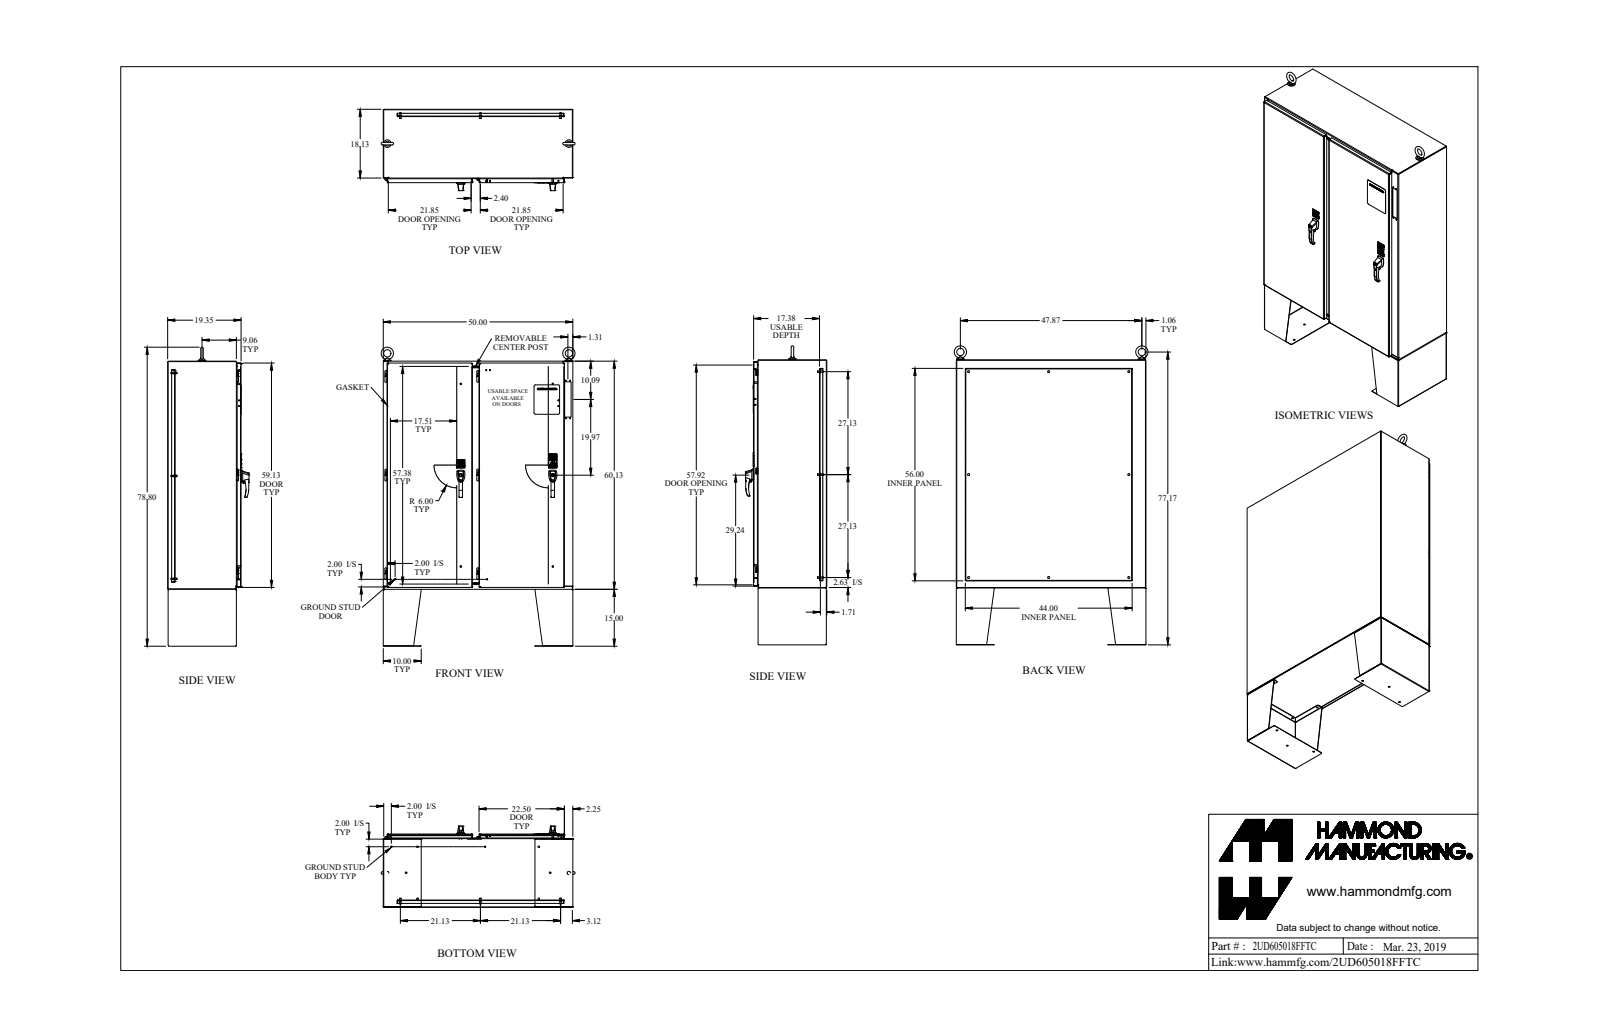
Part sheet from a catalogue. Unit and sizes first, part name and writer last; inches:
Units: inches
Overall size (bounding box): 78.799 × 51.122 × 21.466
Round holes (diameter × count): ⌀0.437 ×14, ⌀0.196 ×11, ⌀0.281 ×11, ⌀0.307 ×11, ⌀0.25 ×10, ⌀0.35 ×8, ⌀0.257 ×6, ⌀0.313 ×6, ⌀0.445 ×5, ⌀0.28 ×4, ⌀0.282 ×4, ⌀0.375 ×4
Round bosses / shafts (diameter × count): ⌀0.25 ×19, ⌀1 ×14, ⌀0.375 ×9, ⌀0.33 ×9, ⌀0.281 ×8, ⌀0.75 ×6, ⌀0.53 ×6, ⌀0.625 ×5
Partial cylindrical surfaces — rounded edges, fillets, slot ends (radius × count): R0.125 ×62, R0.06 ×51, R0.5 ×38, R0.017 ×32, R0.185 ×31, R0.03 ×28, R0.048 ×20, R0.143 ×20
Main face-to-face distances: 0.125, 0.072, 19.293, 19.168, 19.221, 19.096, 1.062, 0.937, 18.159, 18.231
Hole centre spacings: 24.25, 1, 1.125, 7.487, 8.126, 8.675, 16.065, 22.937
Volume: 3 826 in³ · Surface area: 34 309 in²
Bodies: 204 solids, 3153 faces (1855 planar, 928 cylindrical, 370 other)
Part name (STEP PRODUCT): 2UD605018FFTC
STEP written by: SolidWorks 2018 (AUTOMOTIVE_DESIGN)
